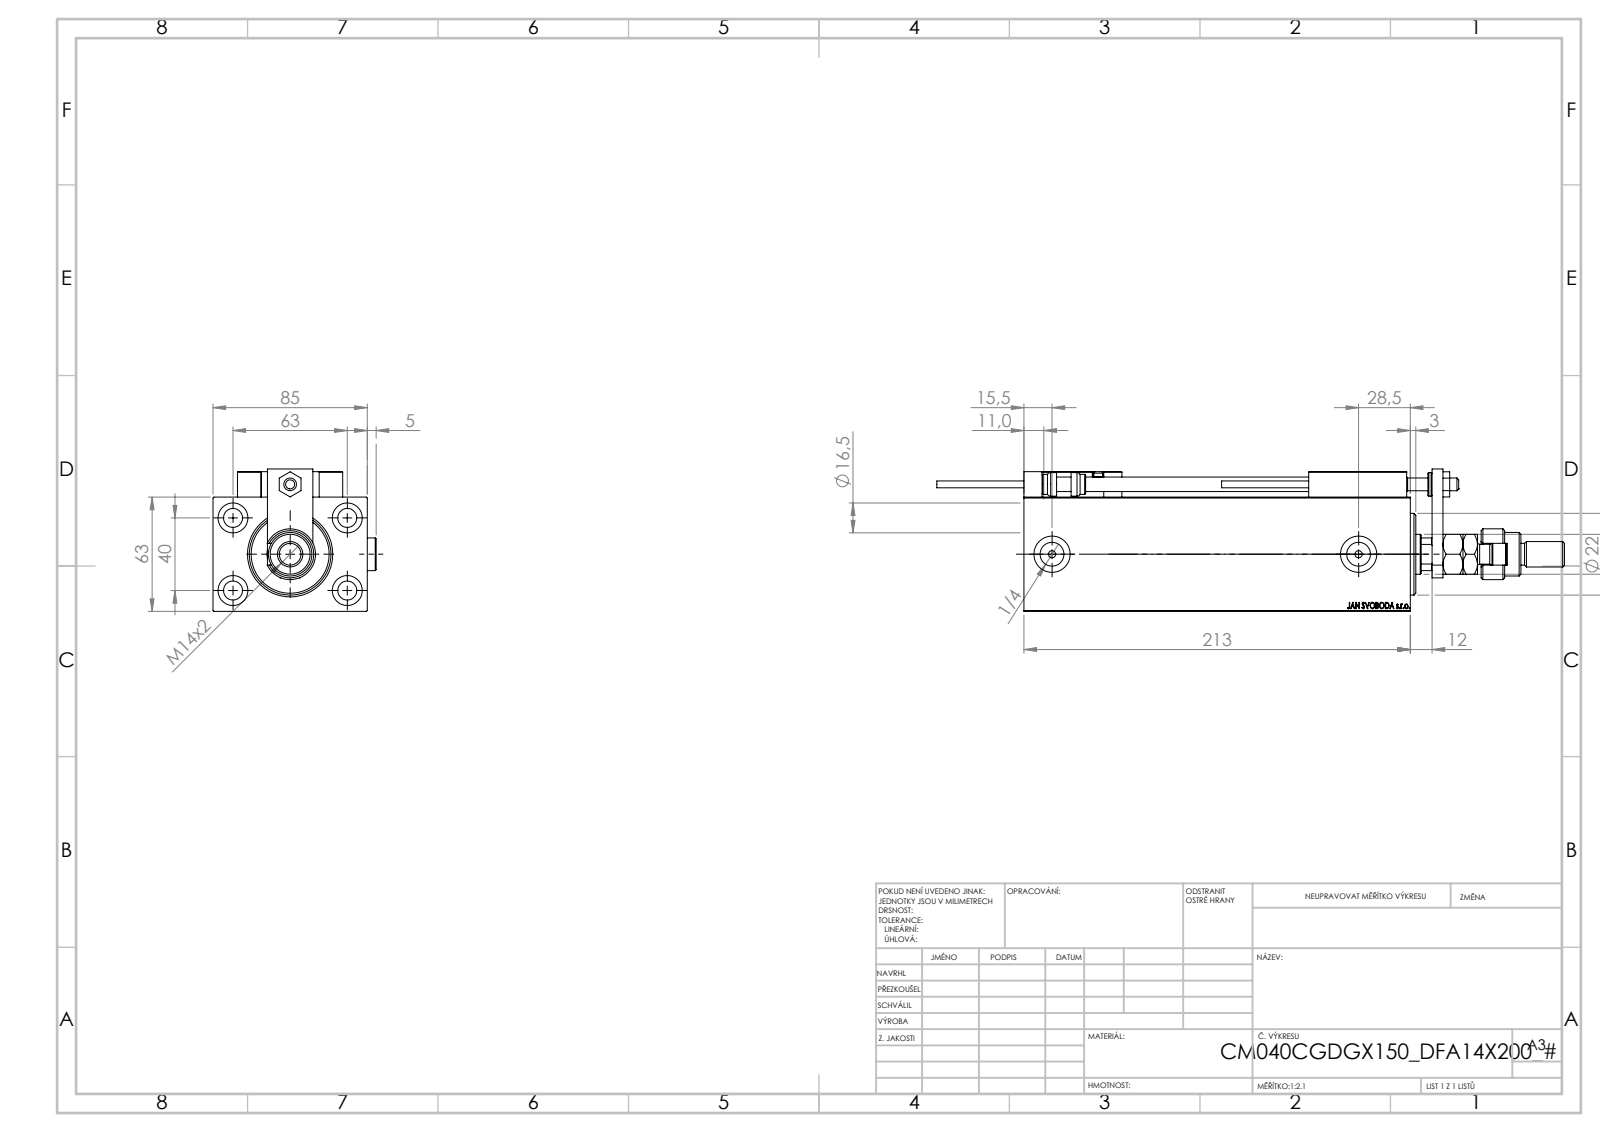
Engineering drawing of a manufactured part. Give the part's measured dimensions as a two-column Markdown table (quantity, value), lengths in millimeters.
| quantity | value |
| --- | --- |
| part name | ALLEN BOLT D5; ALLEN BOLT D8; SWITCH DIM B,W; Zatka_OIL_PORT (+7 more) |
| STEP written by | SolidWorks 2019 (CONFIG_CONTROL_DESIGN) |
| units | millimeters |
| bodies | 27 solids, 1421 faces (622 planar, 217 cylindrical, 582 other) |
| overall size | 346 × 89.9 × 78.5 |
| volume | 1 000 000 mm³ |
| surface area | 193 593 mm² |
| round holes (diameter × count) | 4 × 6, 8 × 5, 16.5 × 5, 3.2 × 4, 10.5 × 4, 5 × 2, 13.16 × 2, 20 × 2, 7 × 1, 12.5 × 1, 22 × 1, 25.5 × 1 |
| round bosses / shafts (diameter × count) | 18 × 3, 11 × 2, 5 × 2, 3.8 × 2, 28 × 1, 24 × 1, 14 × 1, 13 × 1 |
| partial cylindrical surfaces (radius × count) | 0.3 × 30, 3 × 2, 9.75 × 1, 10.5 × 1 |
| main face-to-face distances | 63, 85, 12, 201, 213, 14, 30, 18, 77, 6 |
| hole center spacings | 37.31, 11.37, 20, 29.59, 29.69, 36.06, 36.53, 40 |
